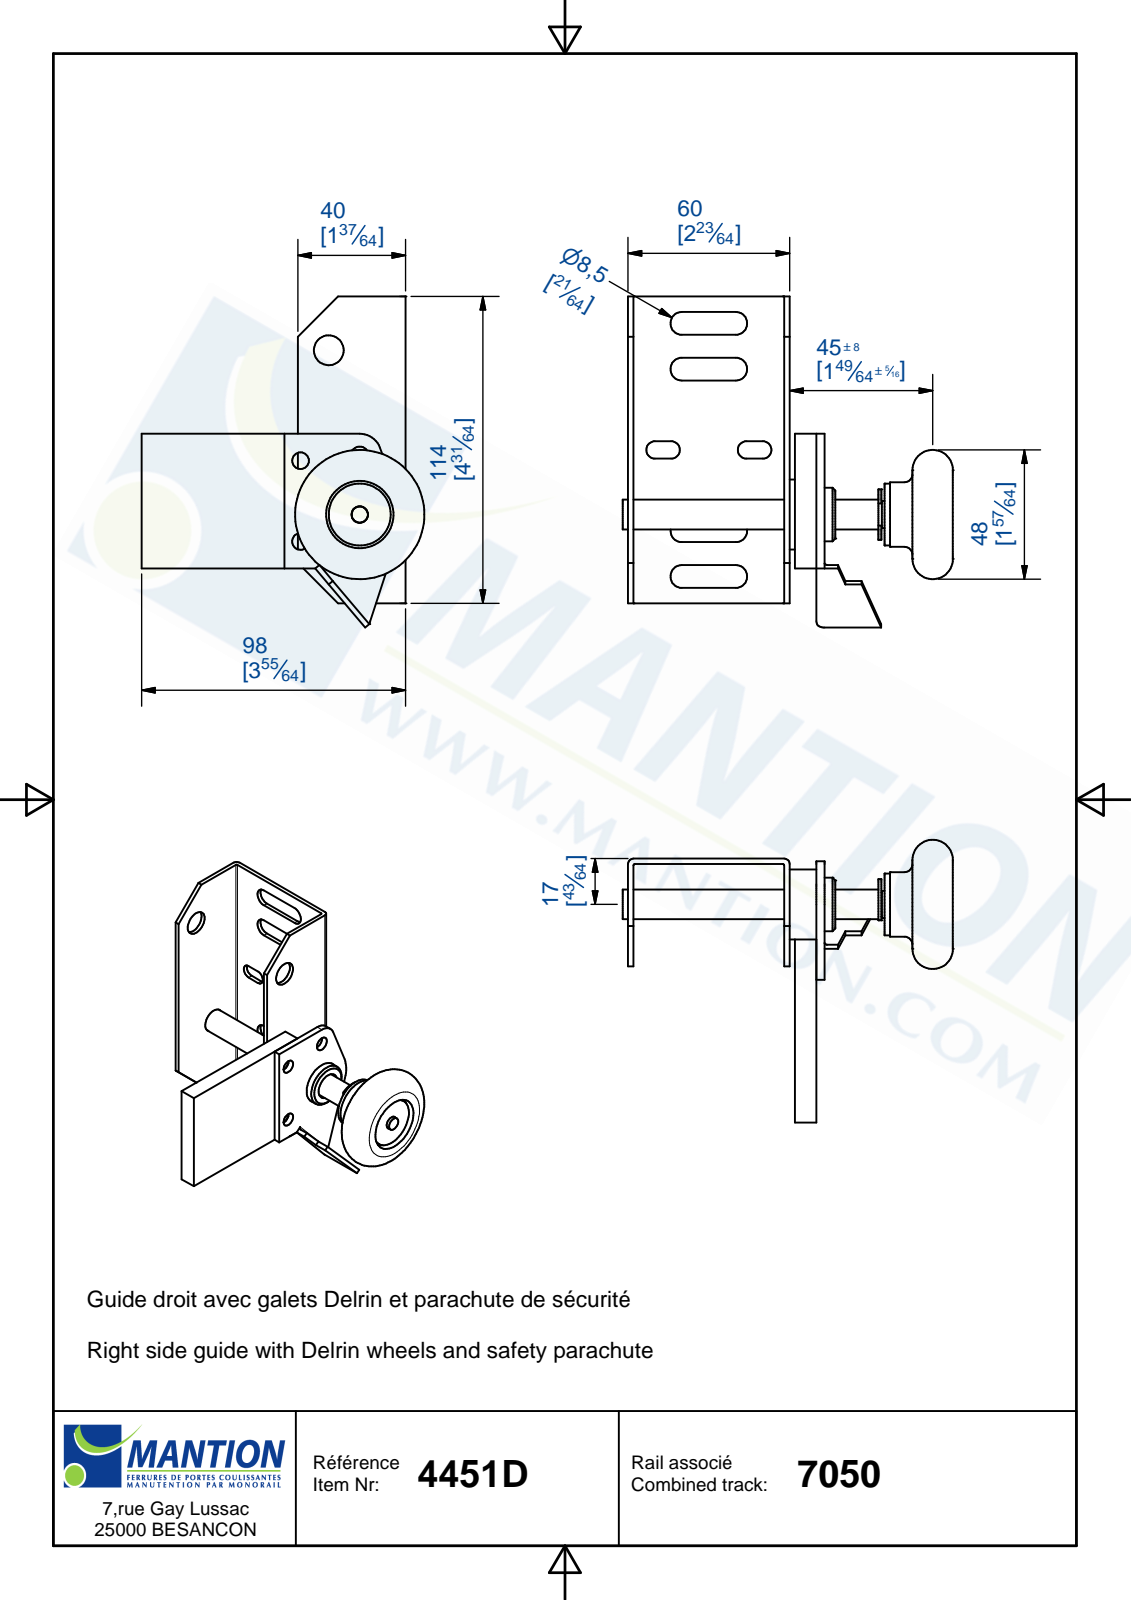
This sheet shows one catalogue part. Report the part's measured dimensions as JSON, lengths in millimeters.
{"part_name": "Pièce1", "step_written_by": "Autodesk Inventor 2017 (AUTOMOTIVE_DESIGN)", "units": "millimeters", "bodies": {"solids": 2, "faces": 249, "planar": 134, "cylindrical": 108, "other": 7}, "overall_size": [123, 122.65, 105], "volume_mm3": 102690, "surface_area_mm2": 57838, "round_holes": [[6.2, 2], [11.1, 2], [4, 1], [6.1, 1], [6.5, 1], [10.2, 1], [16, 1], [20, 1], [25, 1]], "round_bosses_or_shafts": [[3, 9], [6, 3], [26, 1], [24, 1], [23, 1], [19.9, 1], [15.8, 1], [12.2, 1]], "partial_cylinders_radius": [[1.55, 9], [4.25, 8], [3.25, 4], [0.27, 2], [0.5, 2], [0.72, 2], [1.08, 2], [1.35, 2]], "face_to_face_distances": [2, 58, 60, 68, 56, 10, 4, 12, 70, 62], "hole_center_spacings": [22, 22.09, 24.17, 29.73, 30, 38.83, 40.66, 42.32]}
